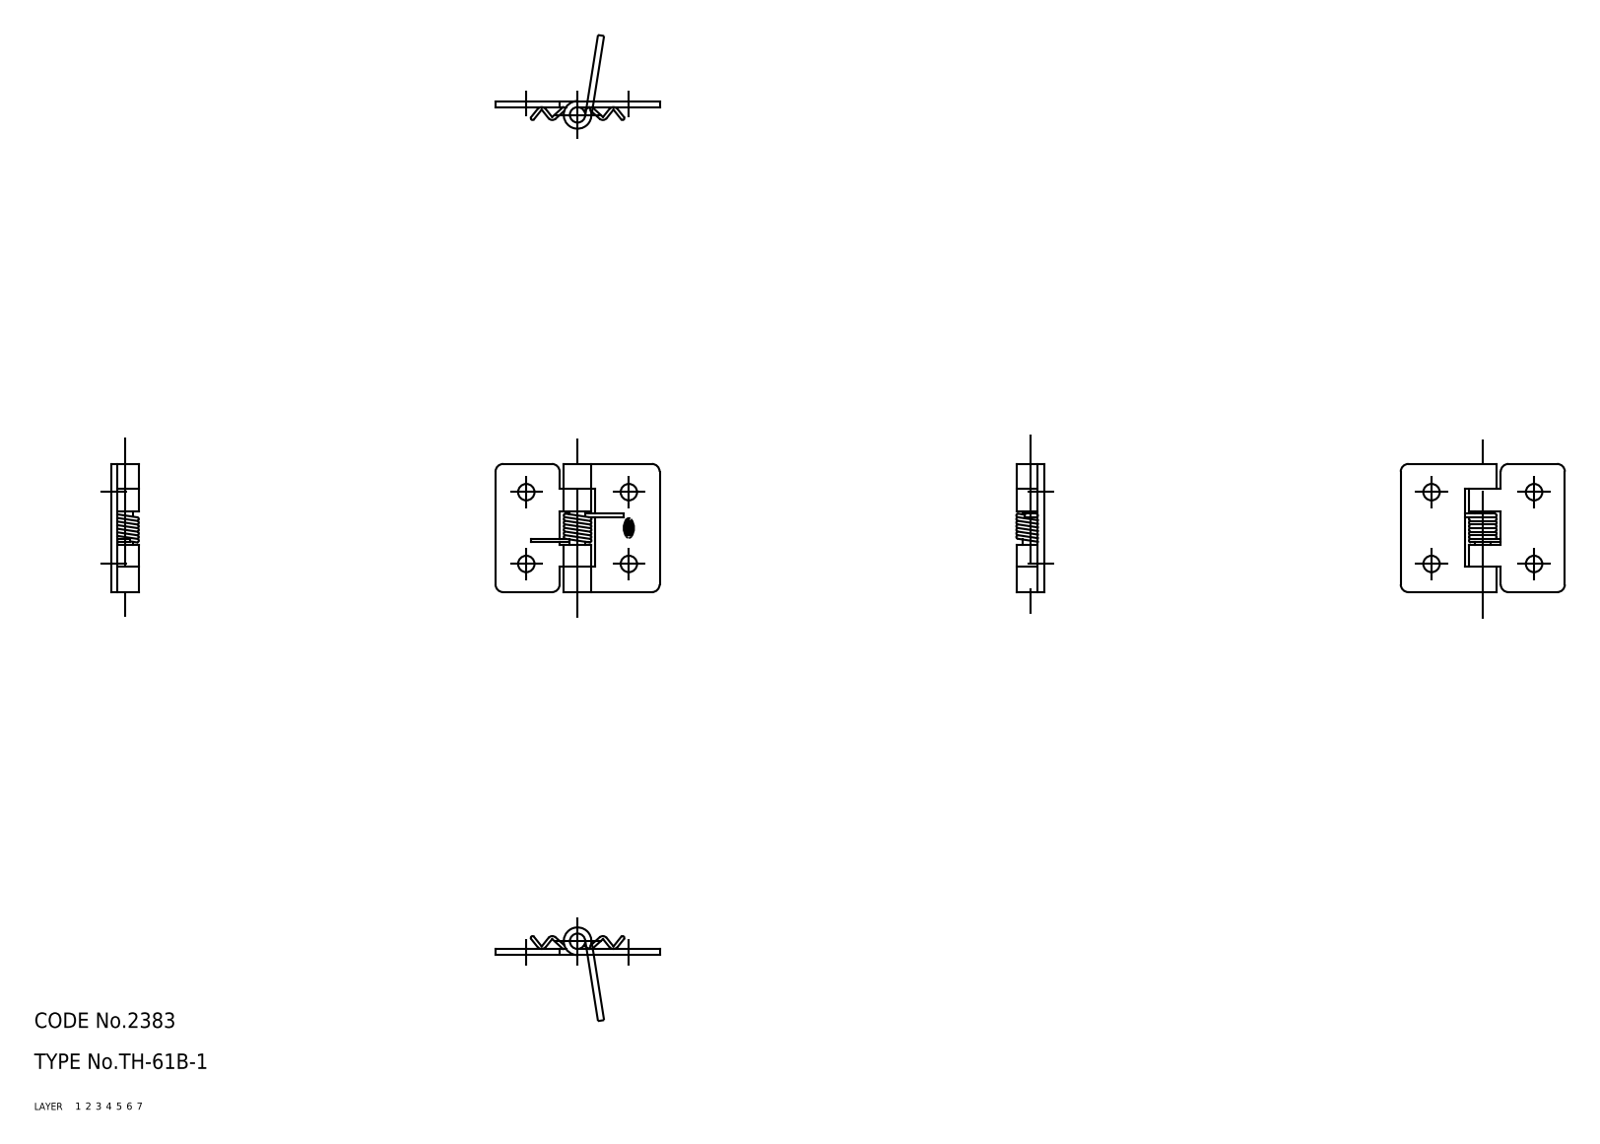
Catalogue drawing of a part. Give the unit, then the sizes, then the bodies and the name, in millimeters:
Units: millimetres
Overall size (bounding box): 32 × 25 × 5.4
Volume: 1 254 mm³ · Surface area: 2 586 mm²
Bodies: 4 solids, 82 faces (0 planar, 0 cylindrical, 82 other)
Part name (STEP PRODUCT): spring; shaft; hinge piece_B; hinge piece_A (+1 more)
STEP written by: CADfix (AUTOMOTIVE_DESIGN)
